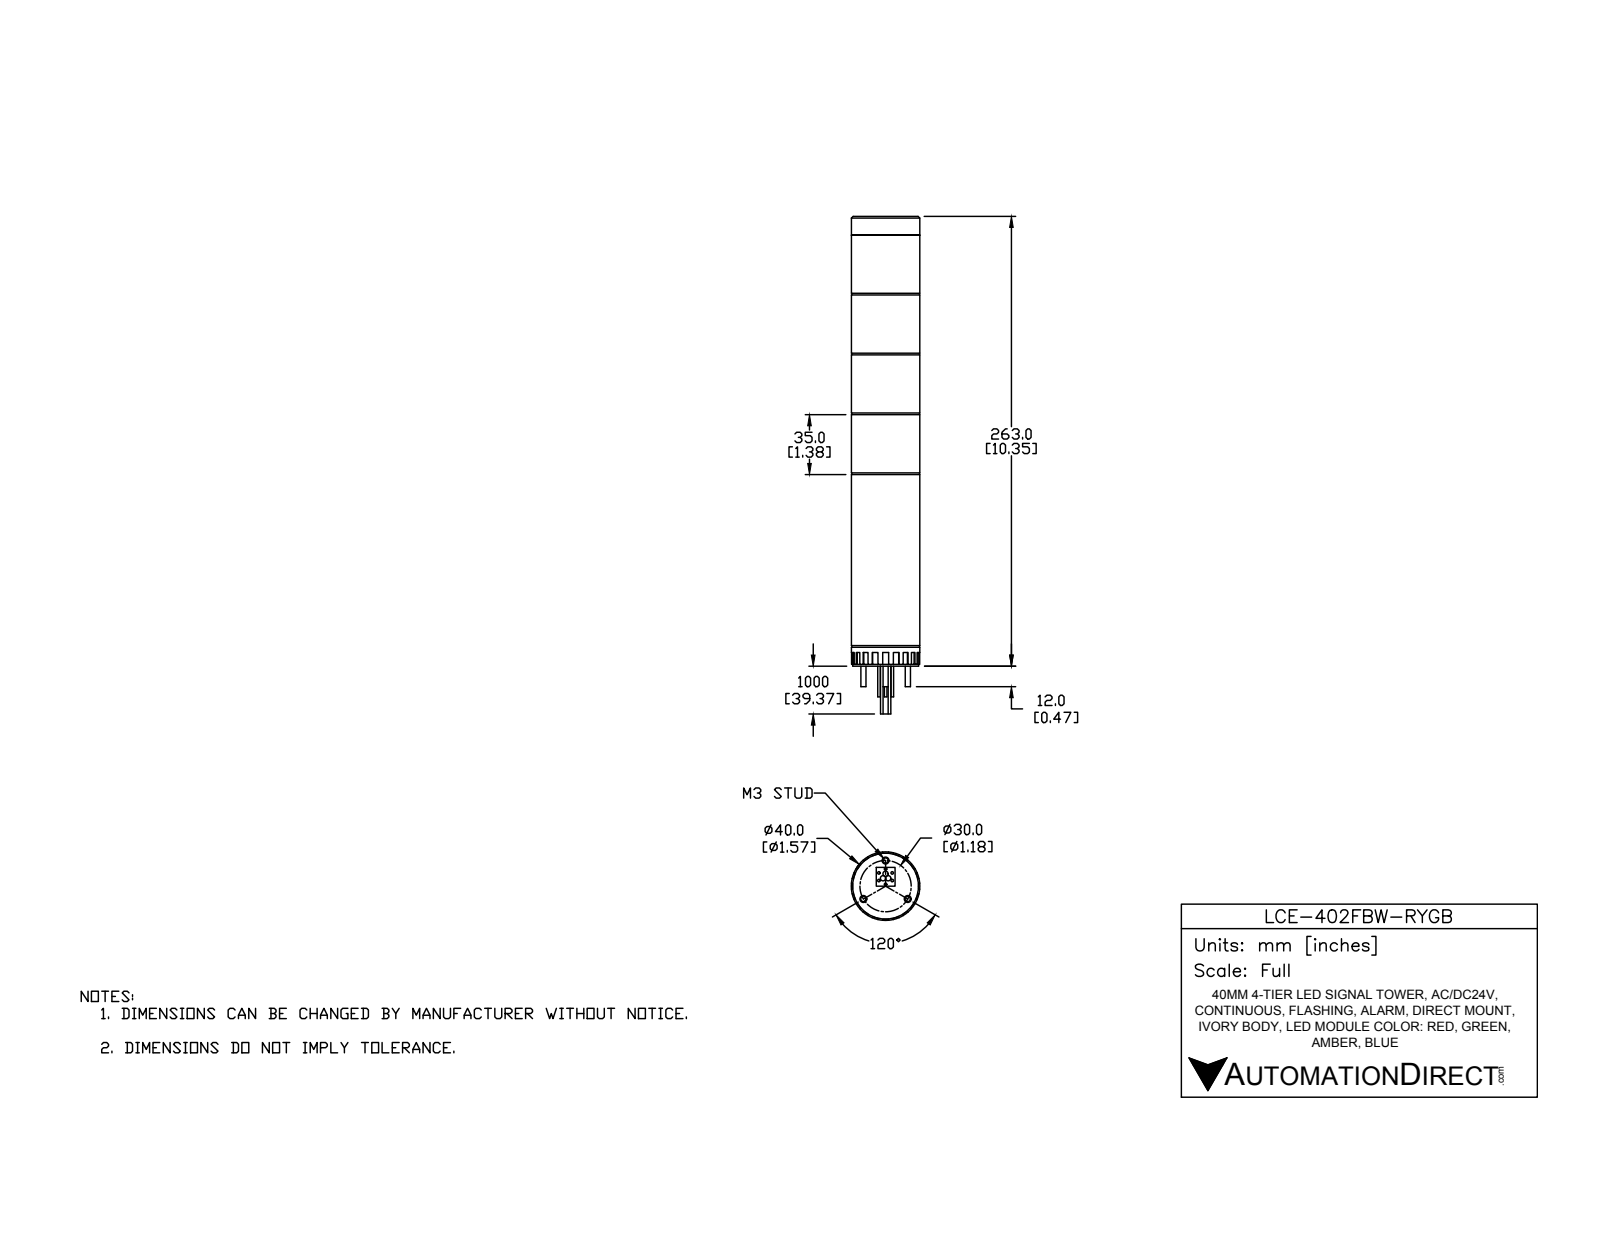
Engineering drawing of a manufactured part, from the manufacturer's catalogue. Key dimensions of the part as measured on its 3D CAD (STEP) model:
Part name (STEP PRODUCT): LCE-402FBW-RYGB
STEP written by: SolidWorks 2016 (AUTOMOTIVE_DESIGN)
Units: millimetres
Bodies: 27 solids, 226 faces (160 planar, 62 cylindrical, 4 other)
Overall size (bounding box): 281 × 40 × 40
Volume: 329 052 mm³ · Surface area: 67 087 mm²
Round holes (diameter × count): ⌀4 ×3, ⌀8 ×1
Round bosses / shafts (diameter × count): ⌀1.5 ×10, ⌀3 ×3, ⌀40 ×1, ⌀39.5 ×1, ⌀38.5 ×1, ⌀5.5 ×1
Main face-to-face distances: 35, 1, 70, 34, 105, 36, 69, 104, 71, 101
Hole centre spacings: 15, 25.98
